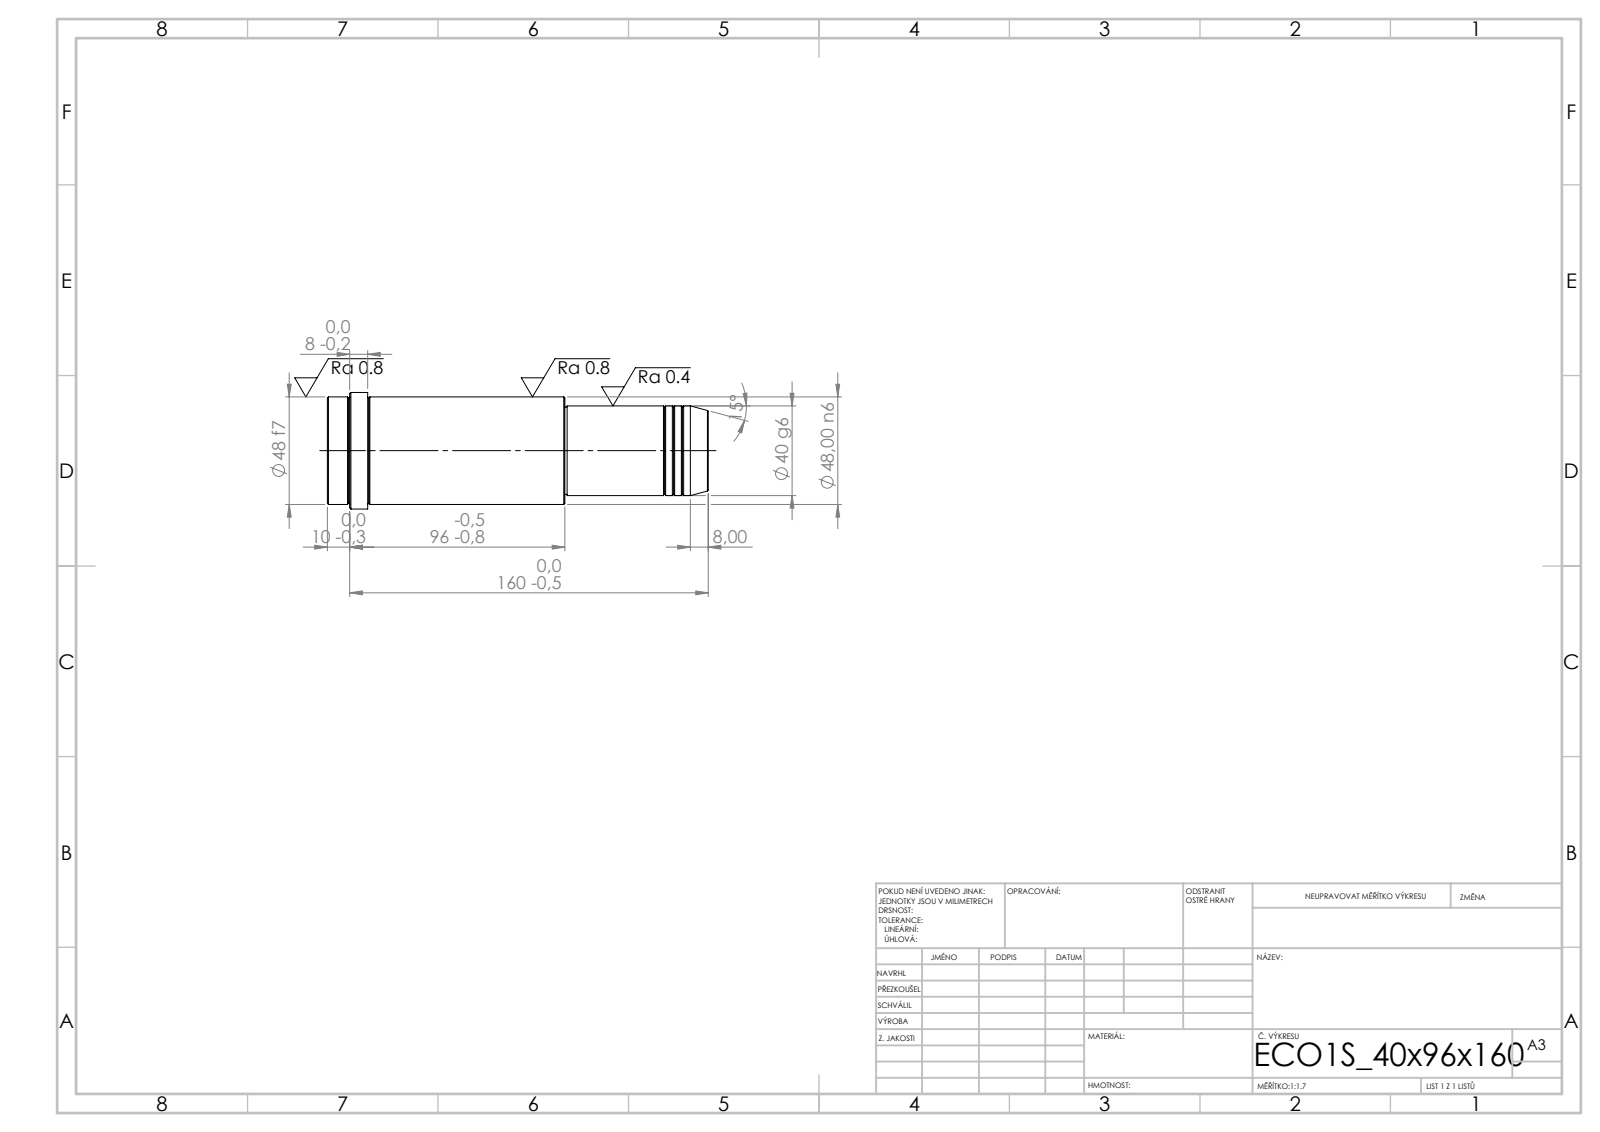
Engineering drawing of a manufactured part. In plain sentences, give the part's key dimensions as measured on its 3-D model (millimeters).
Its 3-D file was written by "SolidWorks 2019 (CONFIG_CONTROL_DESIGN)". It is 1 solid with 52 faces: 6 planar, 16 cylindrical and 30 other. Overall it measures 170 by 52 by 52 millimeters. Its volume is 273 325 cubic millimeters and its surface area 28 442 square millimeters. Round bosses or shafts: 1 of diameter 52, 1 of diameter 48, 1 of diameter 40, 1 of diameter 39. The main face-to-face distances are 170, 64, 106, 152, 88, 18, 160, 96, 8, 10.
